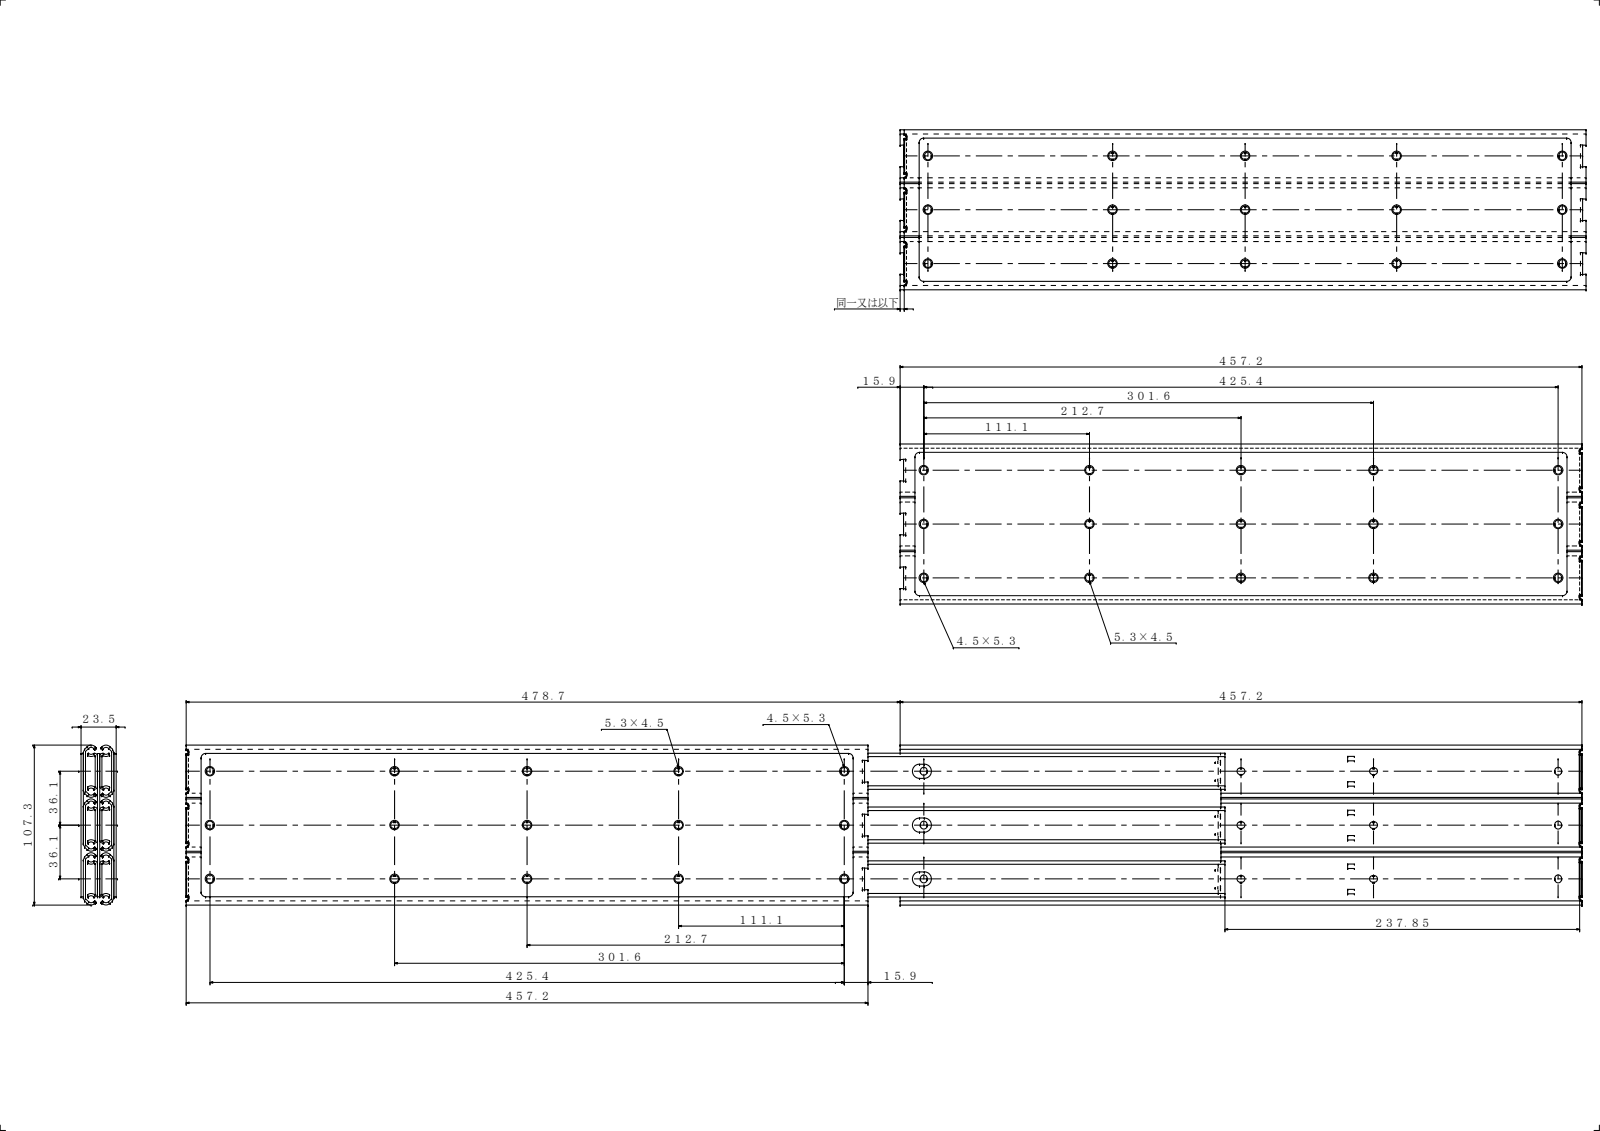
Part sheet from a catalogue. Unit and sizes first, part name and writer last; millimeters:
Units: millimetres
Overall size (bounding box): 935.9 × 107.3 × 23.5
Round holes (diameter × count): ⌀6.4 ×36, ⌀6.5 ×3
Partial cylindrical surfaces — rounded edges, fillets, slot ends (radius × count): R2.25 ×60, R1 ×48, R0.4 ×36, R2 ×36, R3 ×36, R0.3 ×12, R1.3 ×12, R1.83 ×12
Main face-to-face distances: 1.5, 11, 9.5, 20.5, 12.5, 3, 8, 22, 19, 14
Hole centre spacings: 36.1, 72.2, 215.74, 212.7, 156.62, 224.62, 268.44, 328.29
Volume: 512 108 mm³ · Surface area: 708 607 mm²
Bodies: 15 solids, 963 faces (456 planar, 507 cylindrical, 0 other)
Part name (STEP PRODUCT): IM U53-18; IM継板-18; OM U53-18; U53-18 (+1 more)
STEP written by: SolidWorks 2019 (CONFIG_CONTROL_DESIGN)
